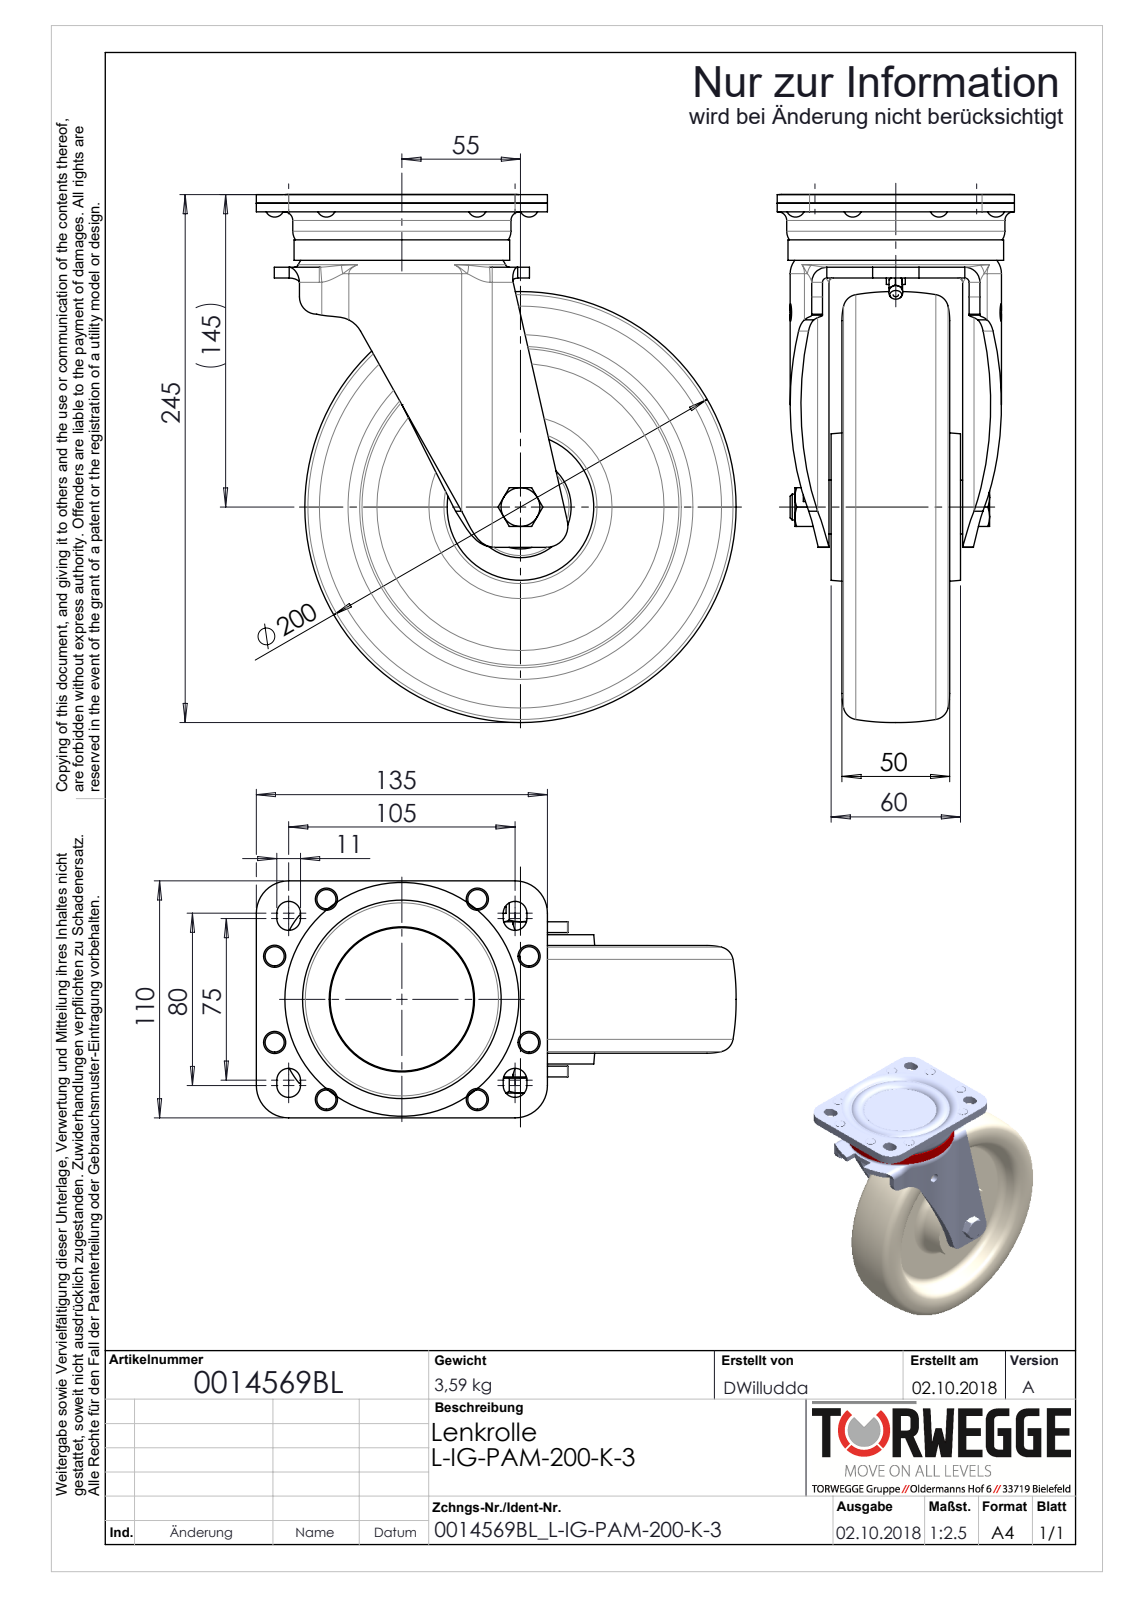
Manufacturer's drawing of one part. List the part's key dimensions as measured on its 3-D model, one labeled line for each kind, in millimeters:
Part name (STEP PRODUCT): 0014569BL_L-IG-PAM-200-K-3
STEP written by: SolidWorks 2016 (AUTOMOTIVE_DESIGN)
Units: millimetres
Bodies: 0 solids, 953 faces (393 planar, 298 cylindrical, 262 other)
Overall size (bounding box): 245.09 × 222.5 × 110
Round holes (diameter × count): ⌀5.3 ×8, ⌀8.2 ×3, ⌀12.2 ×3, ⌀7.8 ×2, ⌀9 ×2, ⌀12.5 ×2, ⌀8 ×1, ⌀10.2 ×1, ⌀12 ×1, ⌀12.3 ×1, ⌀17 ×1, ⌀18 ×1
Round bosses / shafts (diameter × count): ⌀20 ×2, ⌀12 ×2, ⌀100 ×1, ⌀93.2 ×1, ⌀82 ×1, ⌀79 ×1, ⌀47 ×1, ⌀28.1 ×1
Partial cylindrical surfaces — rounded edges, fillets, slot ends (radius × count): R0.37 ×8, R5.5 ×8, R0.21 ×7, R0.62 ×7, R0.12 ×4, R0.86 ×4, R0.93 ×4, R2 ×4
Main face-to-face distances: 11, 5, 4, 6, 22.7, 1, 16.7, 3.92, 25.5, 30.5
Hole centre spacings: 25.09, 35.75, 58.2, 62.3, 70.7, 97.66, 115.14, 33.45
